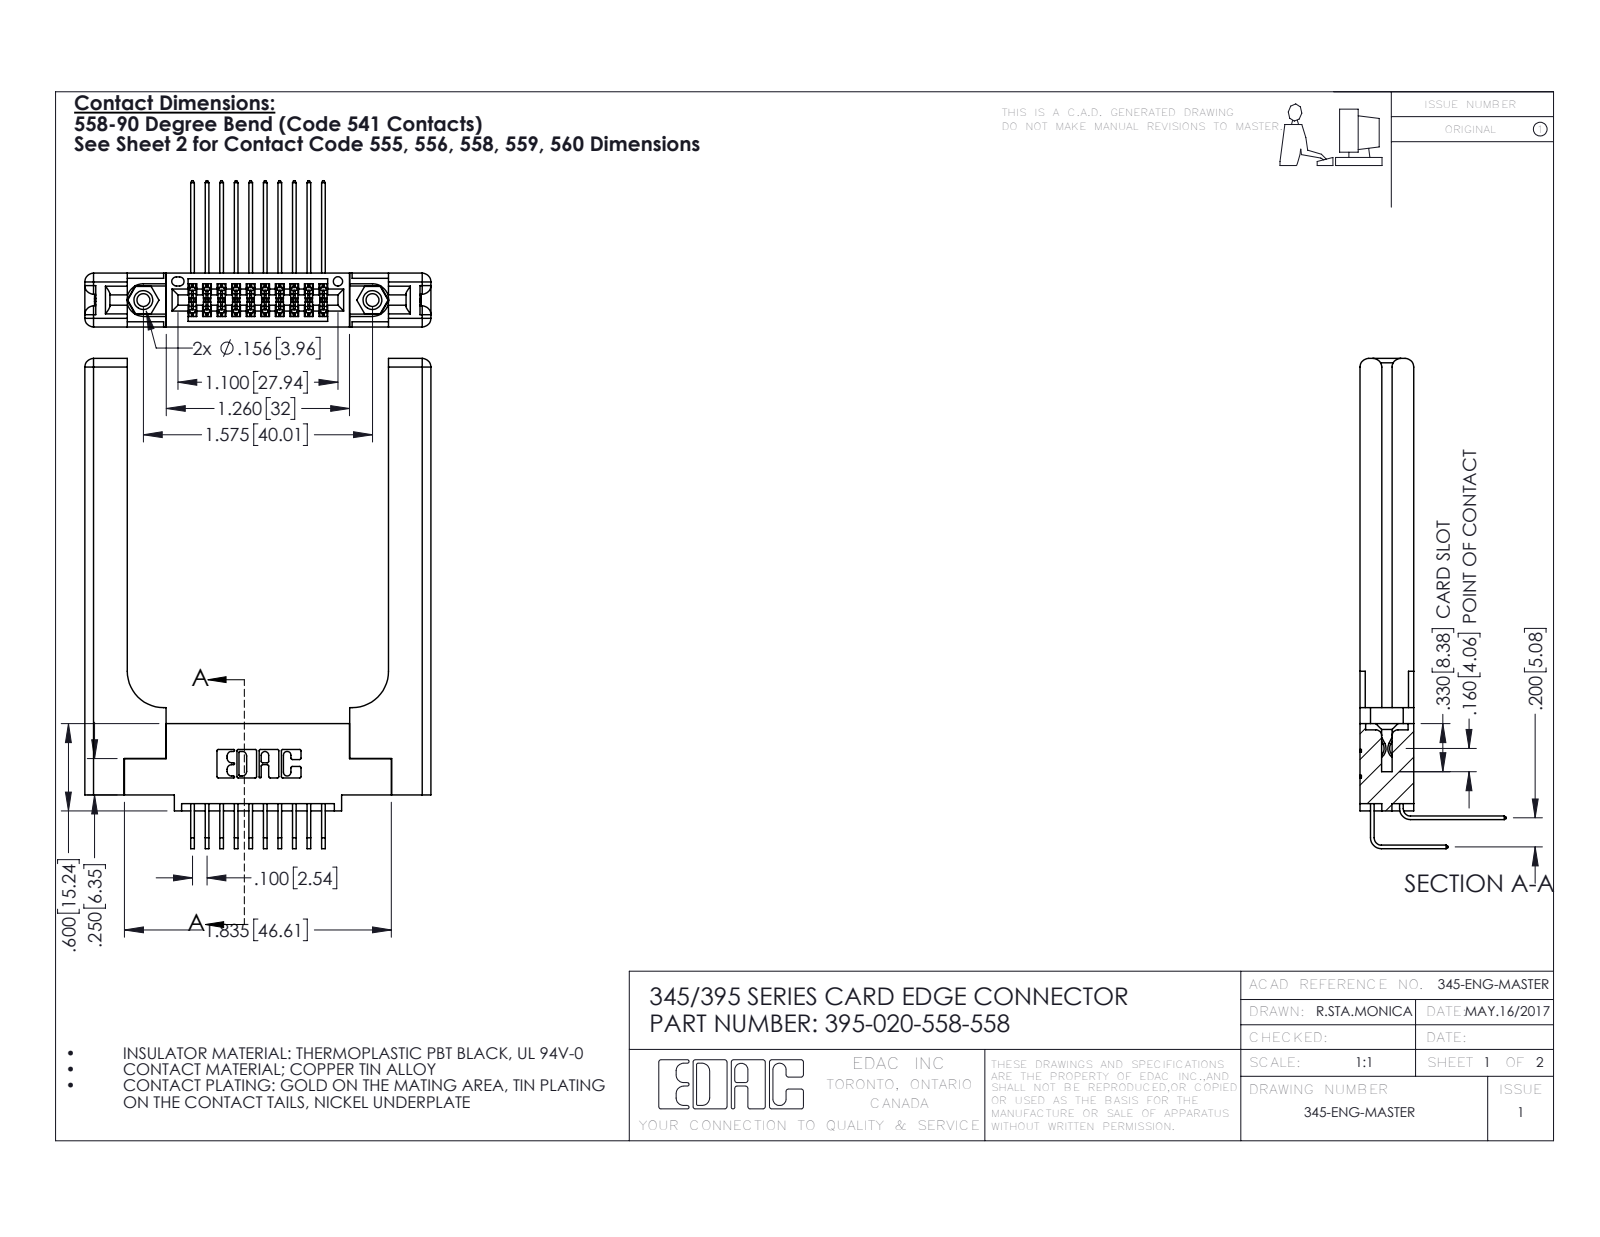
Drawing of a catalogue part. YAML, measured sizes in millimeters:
part_name: "345-220-058_345-220-058; 345-250-001_345-250-001-102; 345-292-001_558 559 Tail - 1; 395-020-558-558 (+2 more)"
step_written_by: "SolidWorks 2016 (CONFIG_CONTROL_DESIGN)"
units: millimeters
bodies: {solids: 25, faces: 1426, planar: 932, cylindrical: 434, other: 60}
overall_size: [85.6, 60.4, 25.5]
volume: 14100
surface_area: 13370
round_holes:
  - {diameter: 2.3, count: 2}
  - {diameter: 3.2, count: 2}
  - {diameter: 4, count: 2}
  - {diameter: 1.6, count: 1}
round_bosses_or_shafts:
  - {diameter: 3.9, count: 2}
partial_cylinders:
  - {radius: 0.2, count: 31}
  - {radius: 0.3, count: 22}
  - {radius: 1.5, count: 16}
  - {radius: 0.2, count: 6}
  - {radius: 0.8, count: 6}
  - {radius: 0.7, count: 3}
  - {radius: 0.4, count: 2}
  - {radius: 0.5, count: 2}
face_to_face_distances: [9.4, 1.8, 3.8, 3.8, 2, 5.6, 7.6, 5.1, 45.6, 5.7]
hole_center_spacings: [6.9, 34.1, 40]
